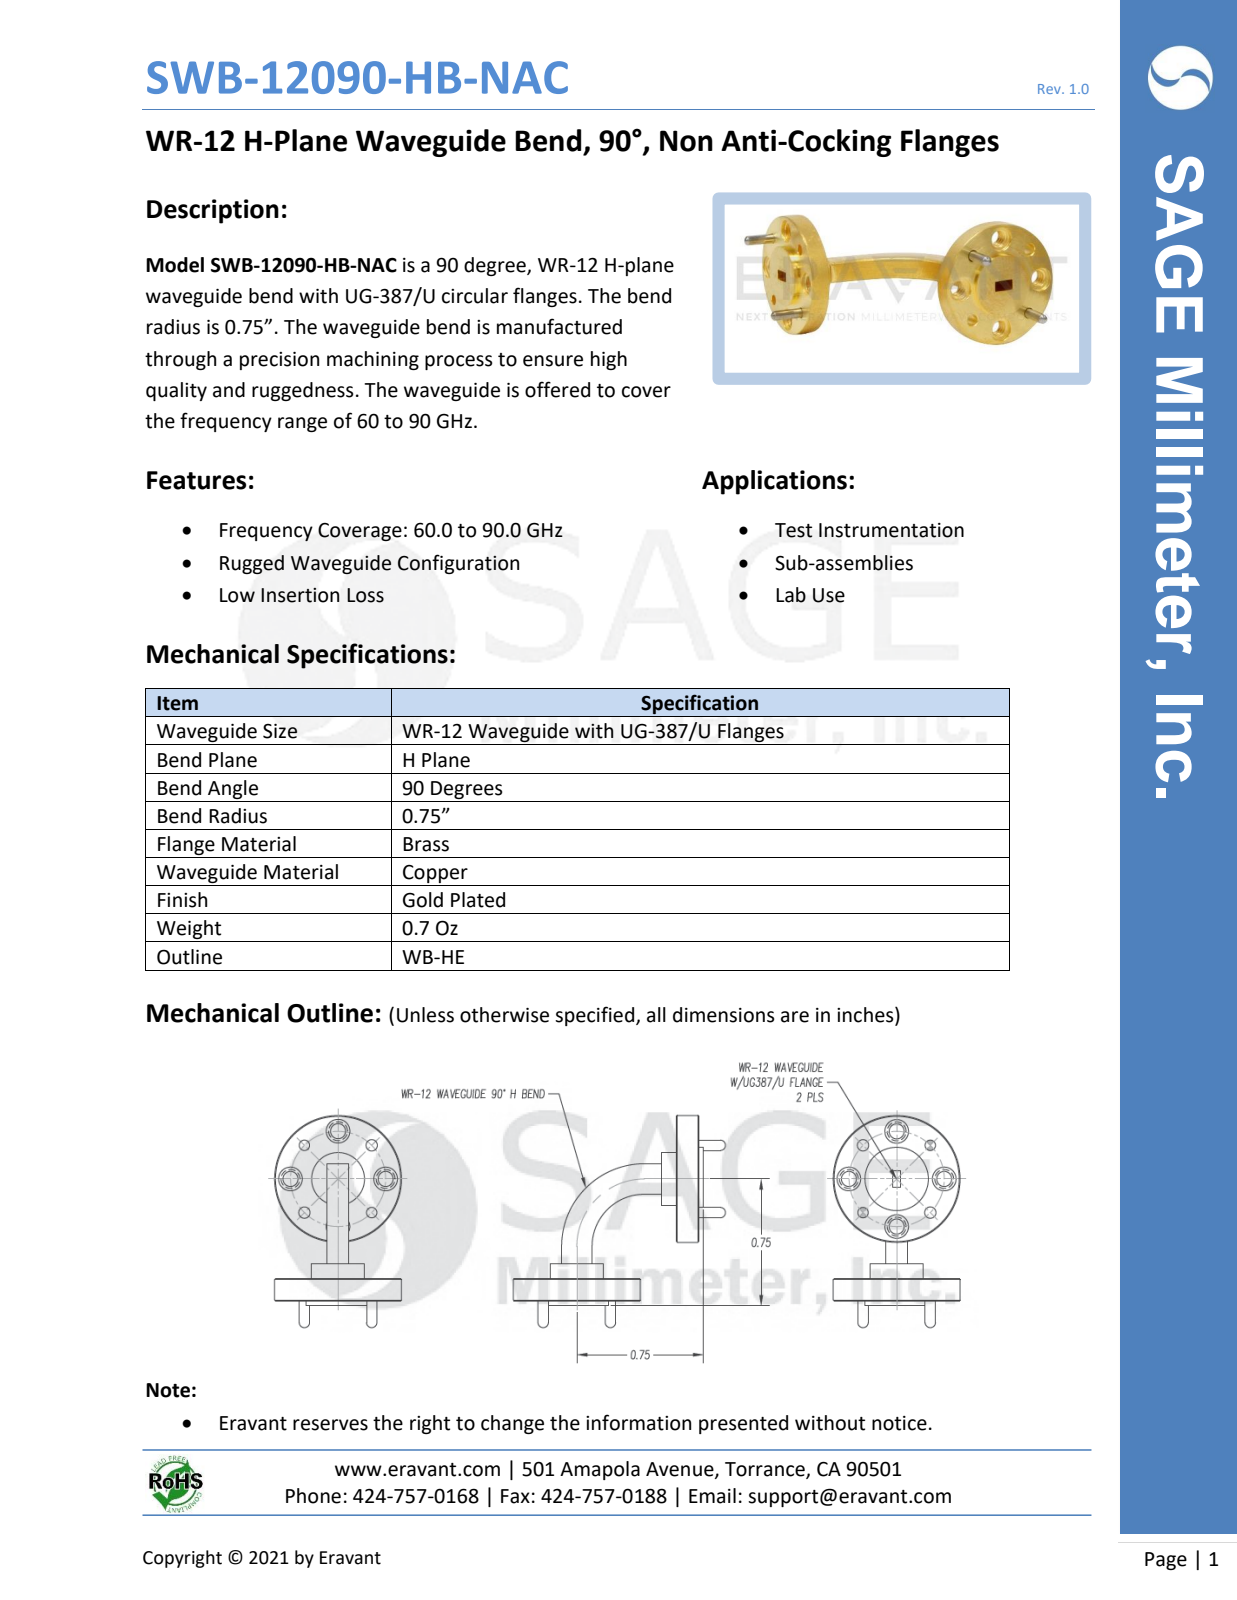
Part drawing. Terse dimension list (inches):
name: WB-HE
written by: SolidWorks 2013 (CONFIG_CONTROL_DESIGN)
unit: in
bodies: 5 solids, 152 faces (40 planar, 72 cylindrical, 40 other)
size: 1.278 × 1.277 × 0.75
volume: 0.147 in³; area: 4.127 in²
holes: 8× ⌀0.089, 8× ⌀0.14, 4× ⌀0.06, 4× ⌀0.067
bosses: 4× ⌀0.063, 2× ⌀0.75, 2× ⌀0.375, 2× ⌀0.35
rounds: 1× R0.399, 1× R0.439, 1× R0.561, 1× R0.601
face distances: 0.13, 0.04, 0.101, 0.03, 0.16, 0.141, 0.26, 0.23, 0.1, 0.061
hole spacings: 0.215, 0.398, 0.519, 0.562
